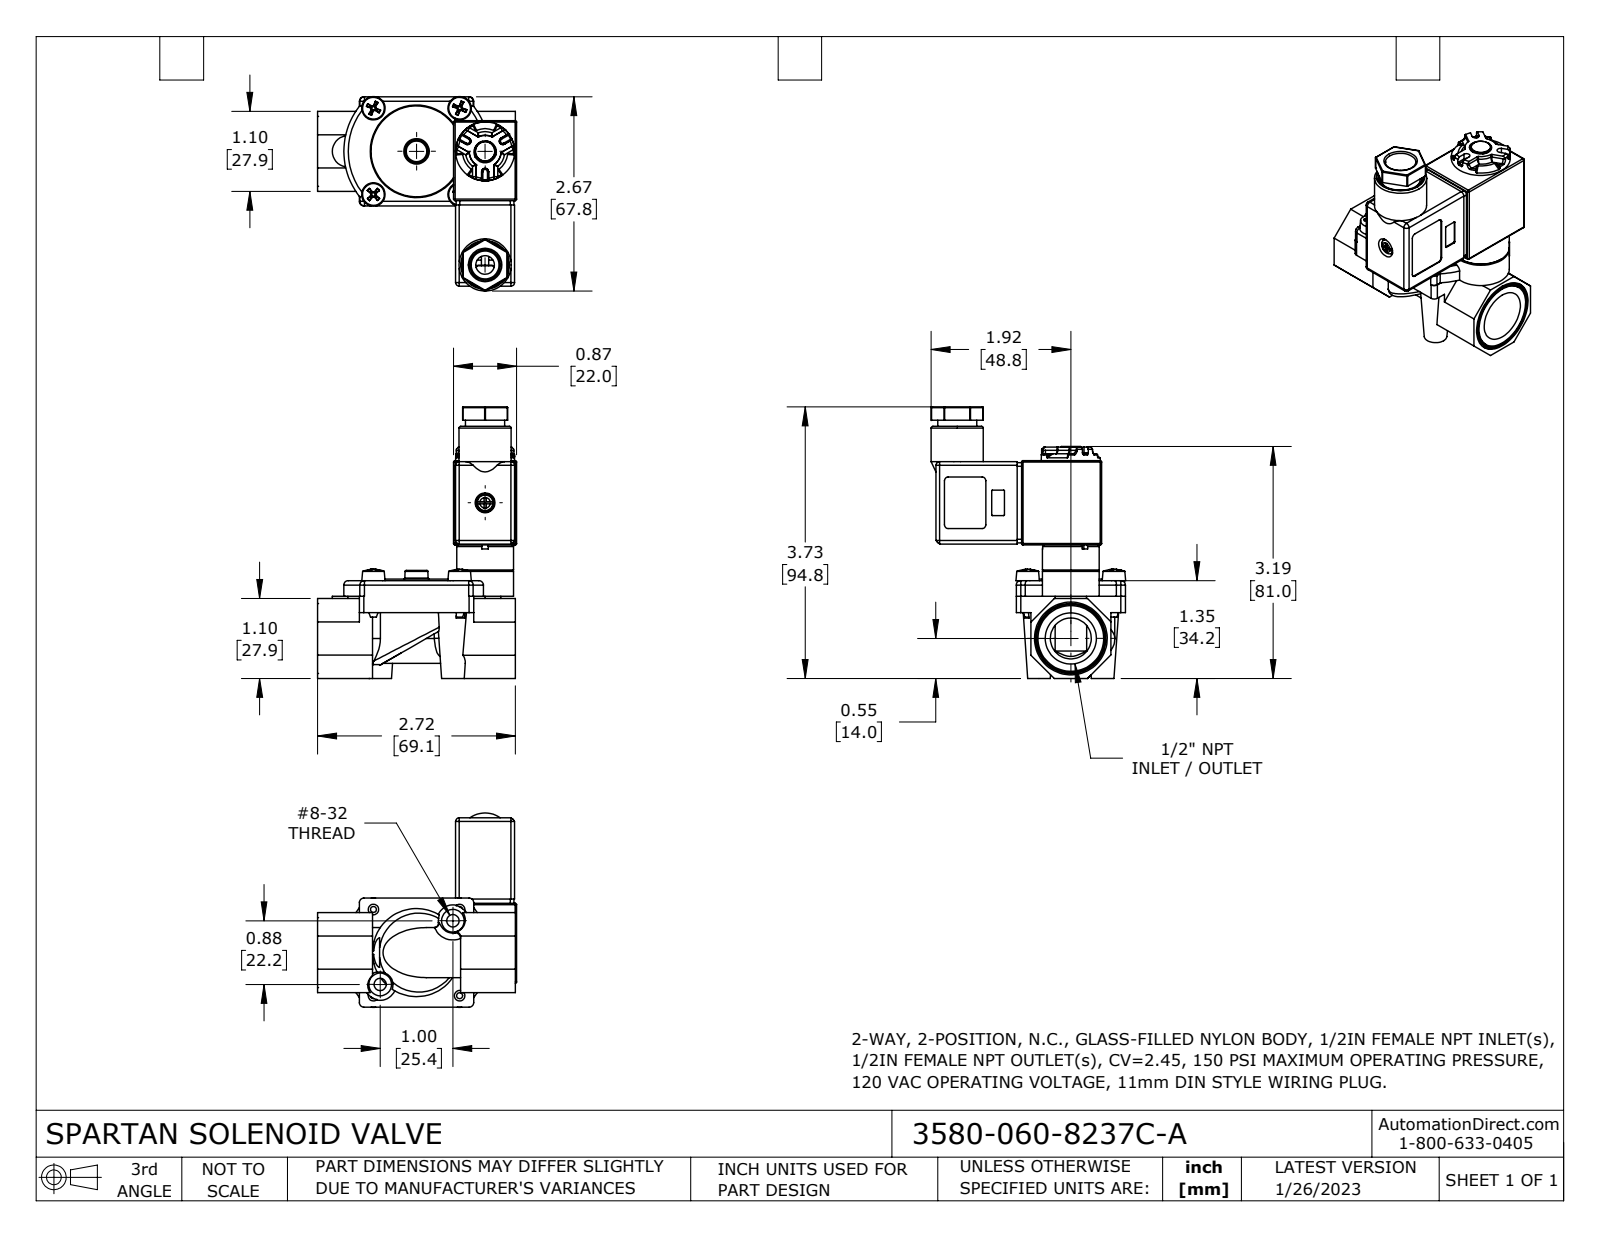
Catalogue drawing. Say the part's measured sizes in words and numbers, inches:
The part is named "3580-060-8237C-A". Its 3-D file was written by "SolidWorks 2021 (CONFIG_CONTROL_DESIGN)". It is 4 solids with 1013 faces: 406 planar, 277 cylindrical and 330 other. Overall it measures 3.731 by 2.736 by 2.674 inches. Its volume is 4.273 cubic inches and its surface area 62.7 square inches. Round holes: 4 of diameter 0.144, 2 of diameter 0.093, 2 of diameter 0.1, 2 of diameter 0.17, 2 of diameter 0.703, 1 of diameter 0.062, 1 of diameter 0.102, 1 of diameter 0.116, 1 of diameter 0.156, 1 of diameter 0.165, 1 of diameter 0.204, 1 of diameter 0.255. Round bosses or shafts: 4 of diameter 0.125, 1 of diameter 1.375, 1 of diameter 0.905, 1 of diameter 0.782, 1 of diameter 0.781, 1 of diameter 0.717, 1 of diameter 0.609, 1 of diameter 0.59. Partial cylindrical surfaces (rounded edges, fillets, slot ends): 24 of radius 0.02, 22 of radius 0.01, 22 of radius 0.05, 12 of radius 0.062, 6 of radius 0.015, 4 of radius 0.035, 3 of radius 0.044, 2 of radius 0.025. The main face-to-face distances are 1.1, 0.06, 0.05, 0.067, 0.683, 0.028, 0.839, 0.866, 0.733, 0.2. The hole center spacings are 0.838, 1.185, 0.181, 0.664, 0.688, 1.034, 1.104, 1.502.
